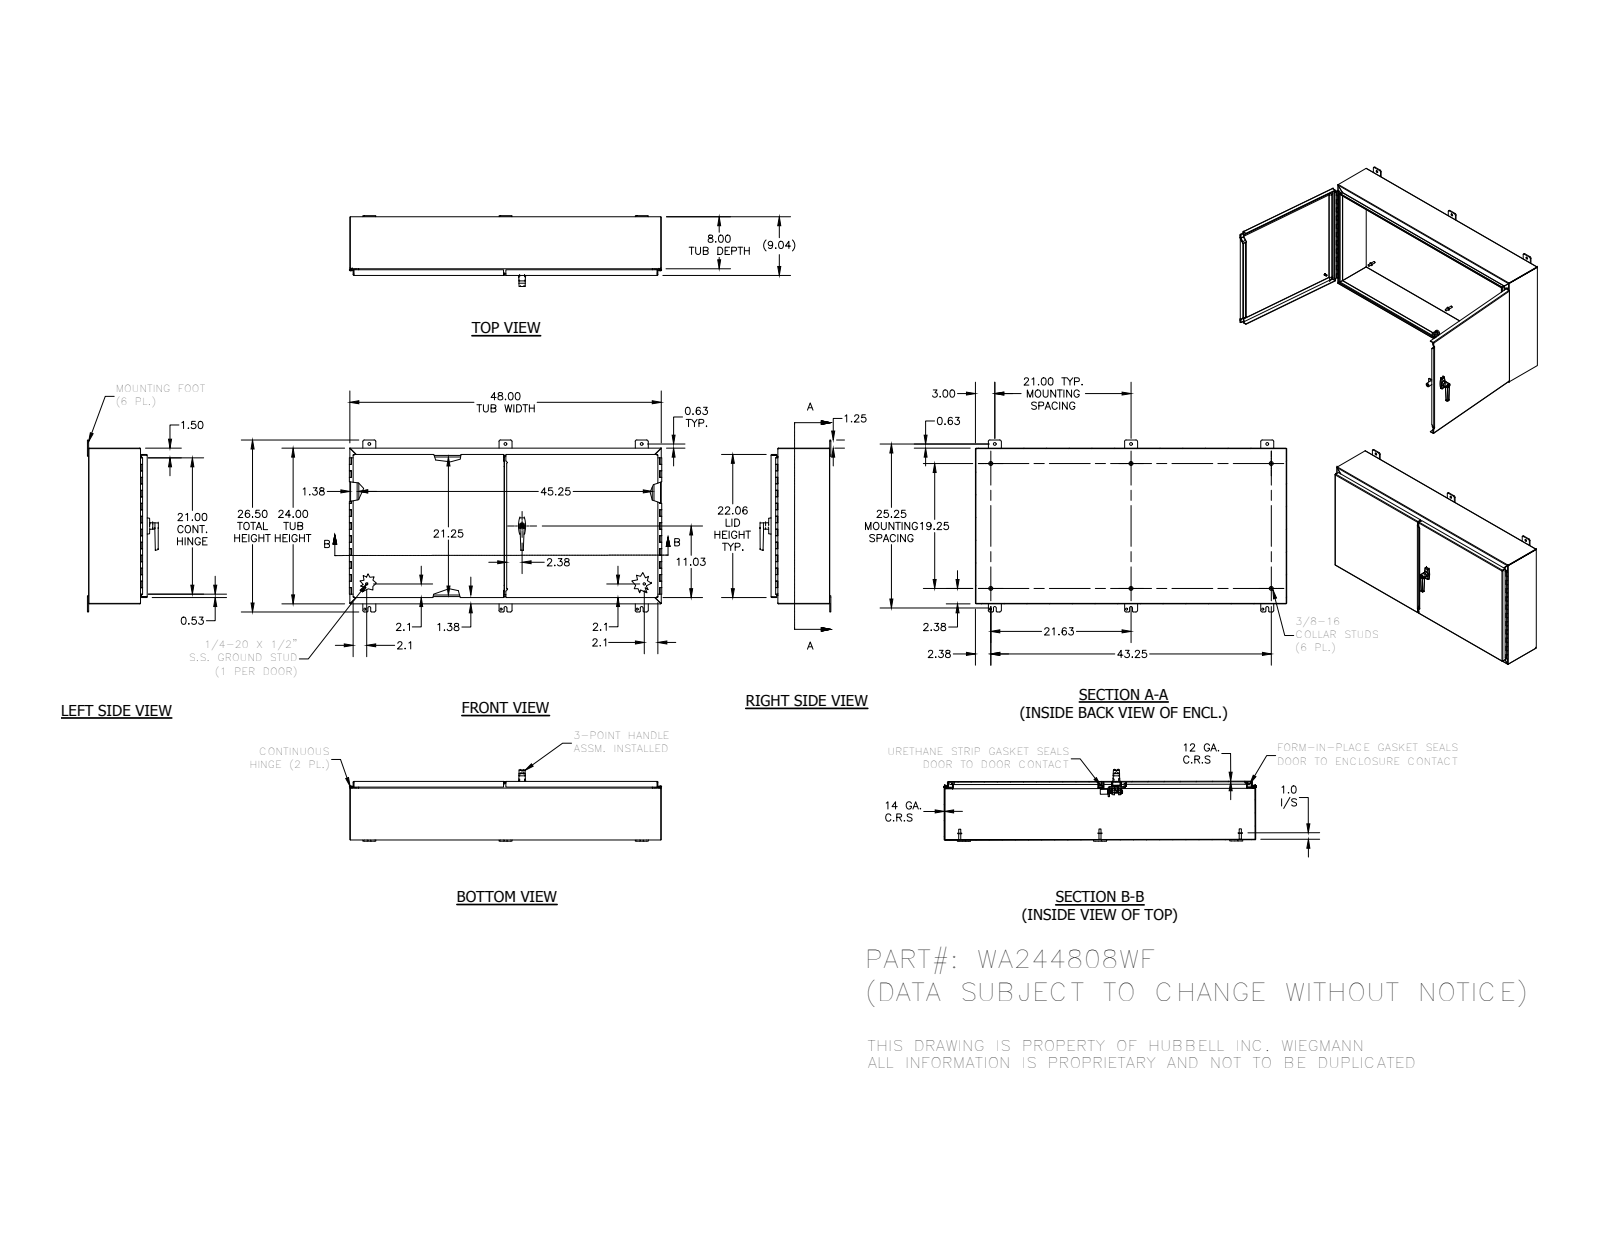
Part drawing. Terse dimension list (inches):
name: WA244808WF; WA244808WFLRS; 34840; WA244808WFBTB (+8 more)
written by: Autodesk Inventor 2012 (AUTOMOTIVE_DESIGN)
unit: in
bodies: 60 solids, 2452 faces (1334 planar, 628 cylindrical, 490 other)
size: 48.148 × 26.5 × 10.919
volume: 363.4 in³; area: 8 435 in²
holes: 8× ⌀0.277, 6× ⌀0.083, 6× ⌀0.313, 6× ⌀0.438, 4× ⌀0.2, 2× ⌀0.125, 2× ⌀0.159, 2× ⌀0.241, 2× ⌀0.25, 2× ⌀0.252, 2× ⌀0.4, 2× ⌀0.407
bosses: 7× ⌀0.157, 6× ⌀0.625, 6× ⌀0.33, 4× ⌀0.25, 4× ⌀0.115, 2× ⌀1, 2× ⌀0.563, 2× ⌀0.527
rounds: 28× R0.031, 24× R0.25, 22× R0.008, 22× R0.016, 17× R0.105, 16× R0.01, 14× R0.05, 12× R0.125
face distances: 0.074, 0.094, 8.942, 8.868, 9.035, 8.961, 23.926, 47.926, 24, 23.852
hole spacings: 21, 31.891, 0.293, 0.201, 20.364, 21.735, 42, 48.374
